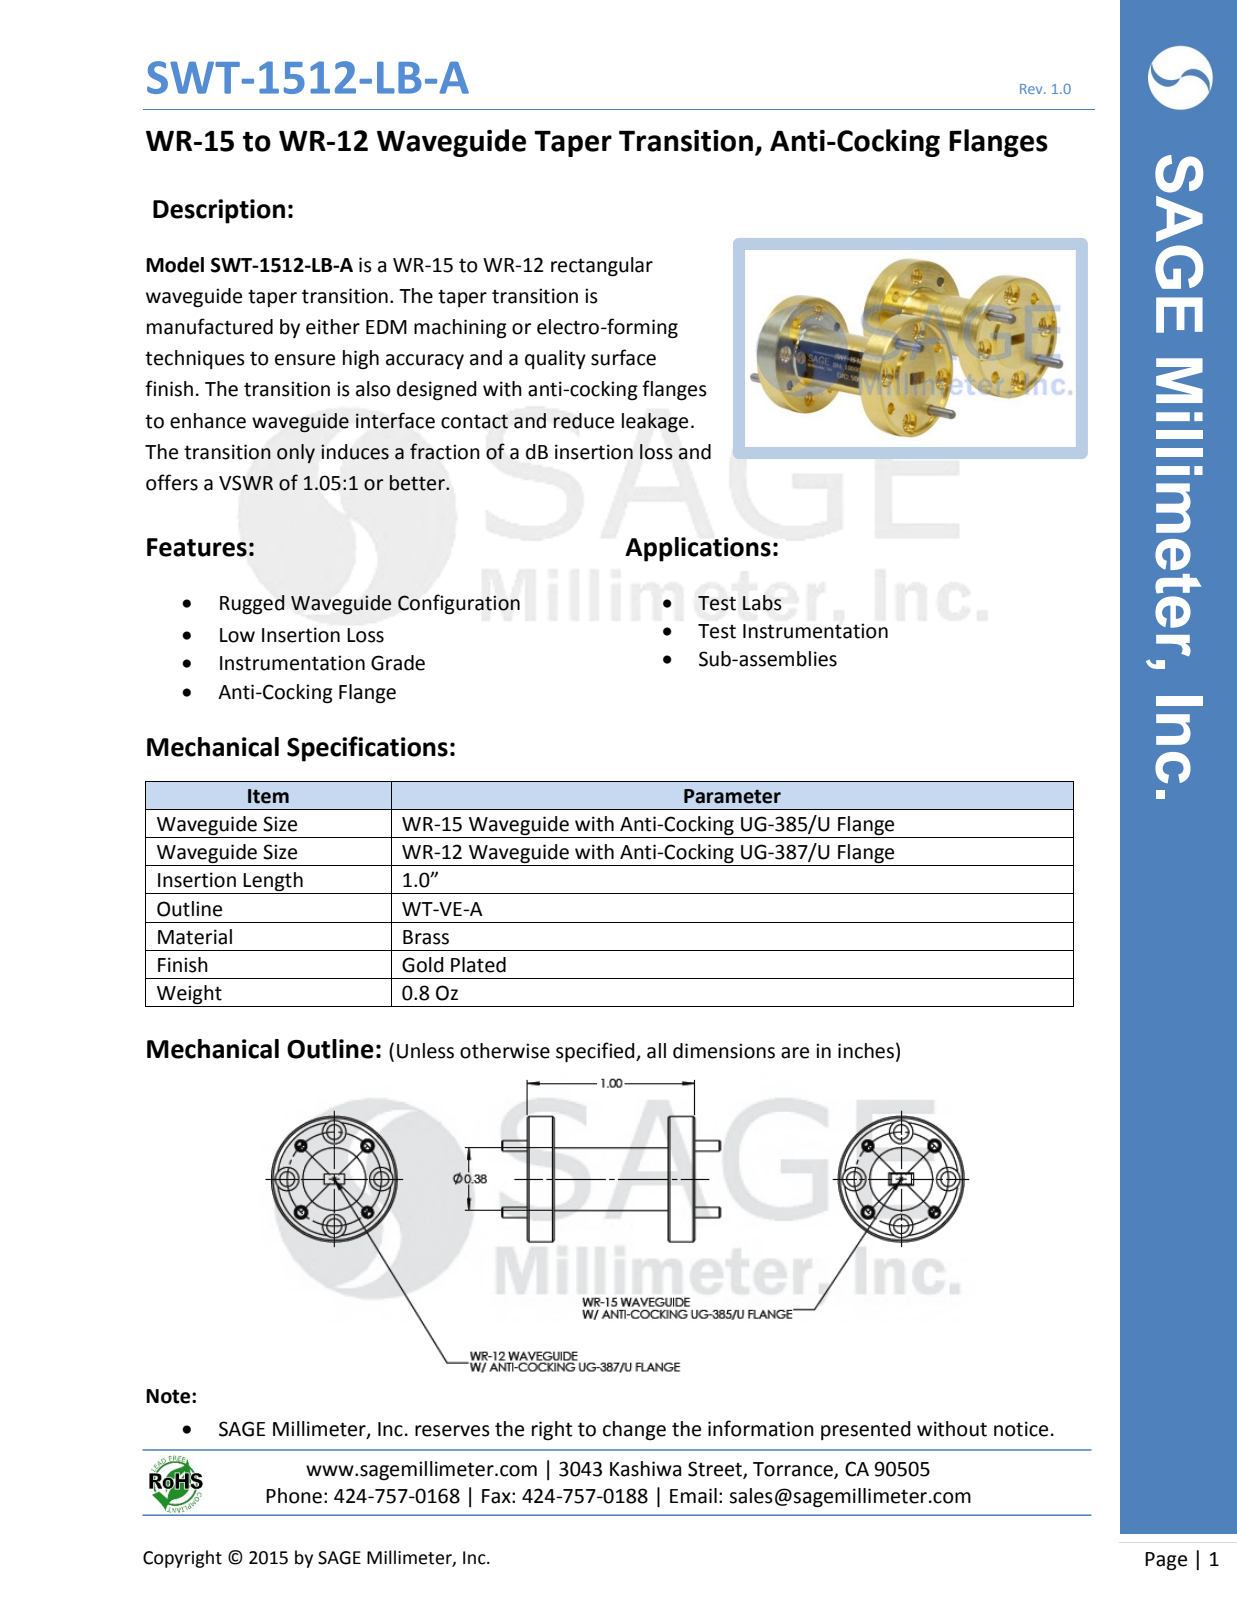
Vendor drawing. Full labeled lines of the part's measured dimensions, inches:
Part name (STEP PRODUCT): SWT-1512-LBA
STEP written by: SolidWorks 2013 (CONFIG_CONTROL_DESIGN)
Units: inches
Bodies: 5 solids, 142 faces (28 planar, 74 cylindrical, 40 other)
Overall size (bounding box): 1.305 × 0.75 × 0.75
Volume: 0.188 in³ · Surface area: 4.249 in²
Round holes (diameter × count): ⌀0.06 ×4, ⌀0.067 ×4, ⌀0.089 ×4, ⌀0.14 ×4, ⌀0.68 ×1
Round bosses / shafts (diameter × count): ⌀0.063 ×4, ⌀0.75 ×1, ⌀0.375 ×1, ⌀0.375 ×1
Main face-to-face distances: 0.14, 0.82, 0.68, 0.96, 0.02, 0.16, 0.84, 0.98, 1, 0.98
Hole centre spacings: 0.215, 0.398, 0.281, 0.519, 0.52, 0.281, 0.562, 0.563
